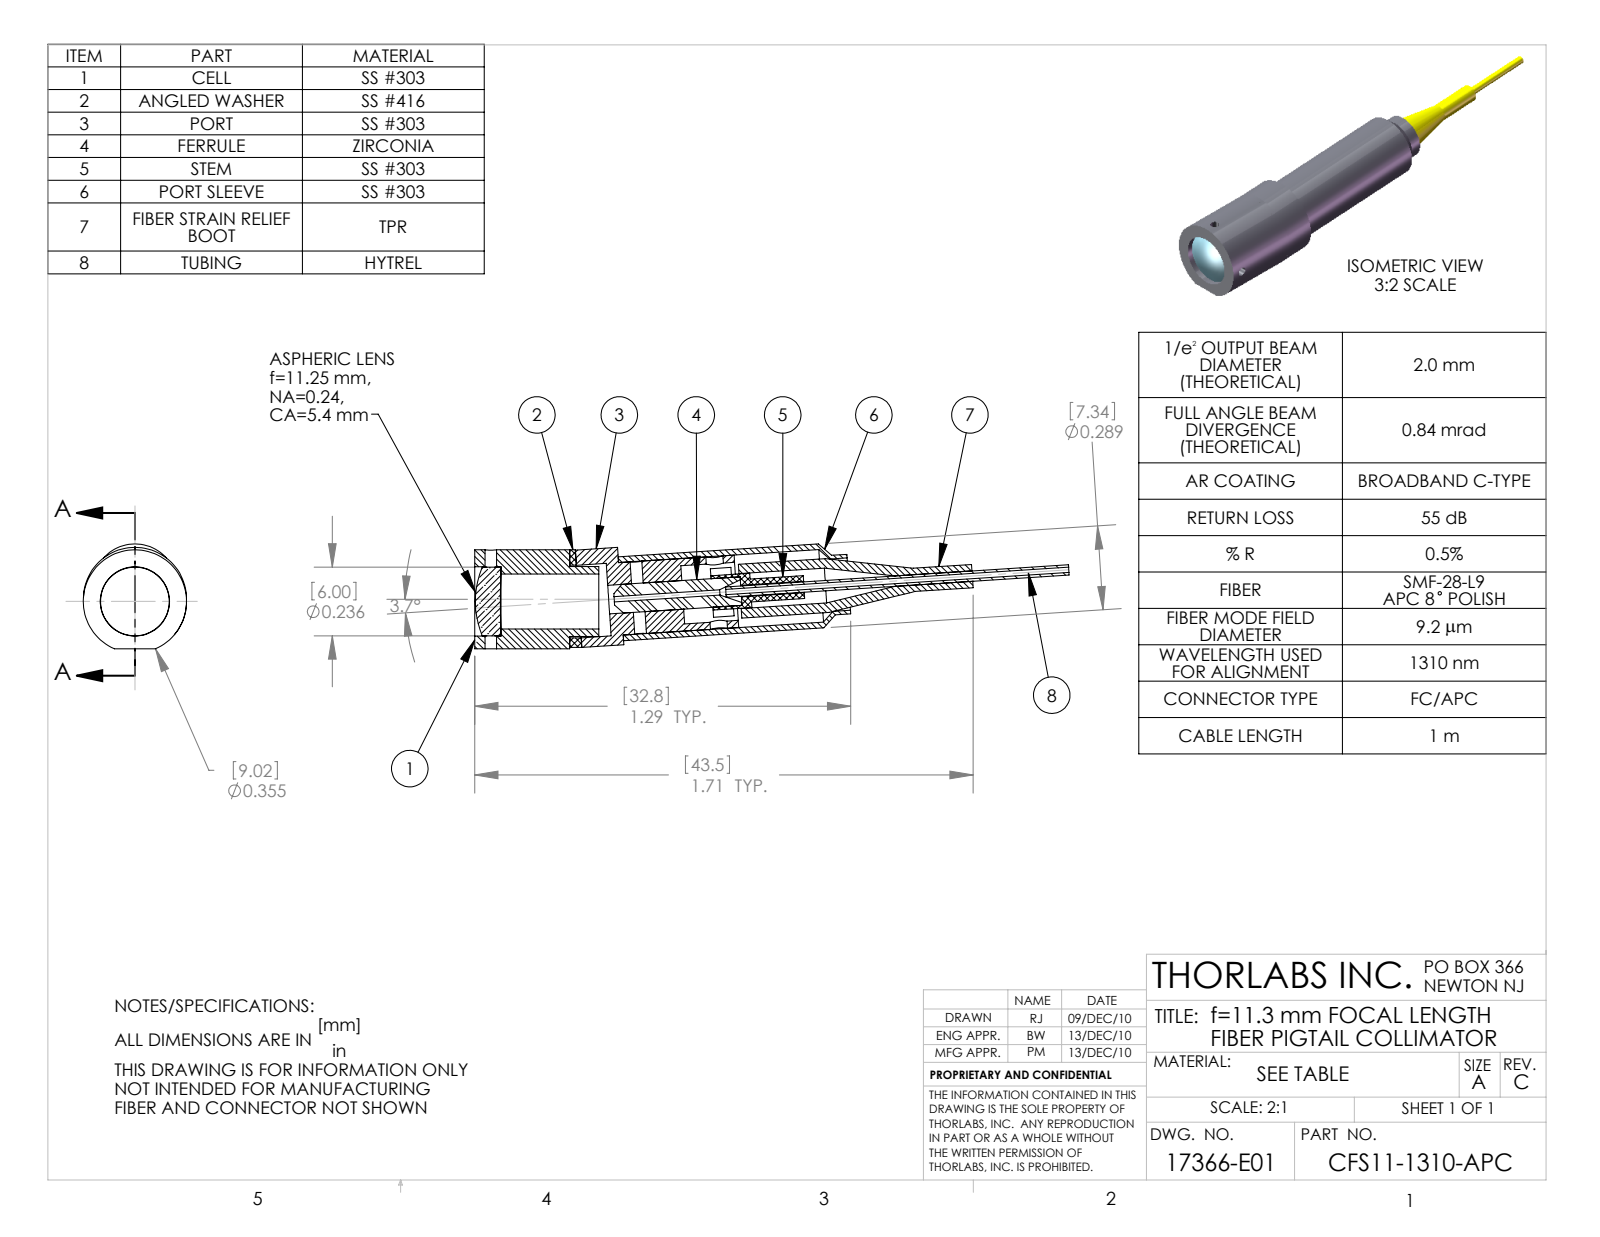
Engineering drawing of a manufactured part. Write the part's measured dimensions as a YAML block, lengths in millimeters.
part_name: "17366-E0W"
step_written_by: "SolidWorks 2009 (AUTOMOTIVE_DESIGN)"
units: millimeters
bodies: {solids: 0, faces: 51, planar: 12, cylindrical: 33, other: 6}
overall_size: [51.89, 9.16, 9.02]
round_holes:
  - {diameter: 1.02, count: 2}
  - {diameter: 0.46, count: 1}
  - {diameter: 0.91, count: 1}
  - {diameter: 4.57, count: 1}
  - {diameter: 6.05, count: 1}
round_bosses_or_shafts:
  - {diameter: 9.02, count: 1}
  - {diameter: 9, count: 1}
  - {diameter: 7.34, count: 1}
  - {diameter: 5.21, count: 1}
  - {diameter: 2.03, count: 1}
  - {diameter: 0.9, count: 1}
face_to_face_distances: [8.28, 3.69, 23.63, 19.94, 34.44, 30.75, 10.81, 42.88, 39.19, 19.25]
